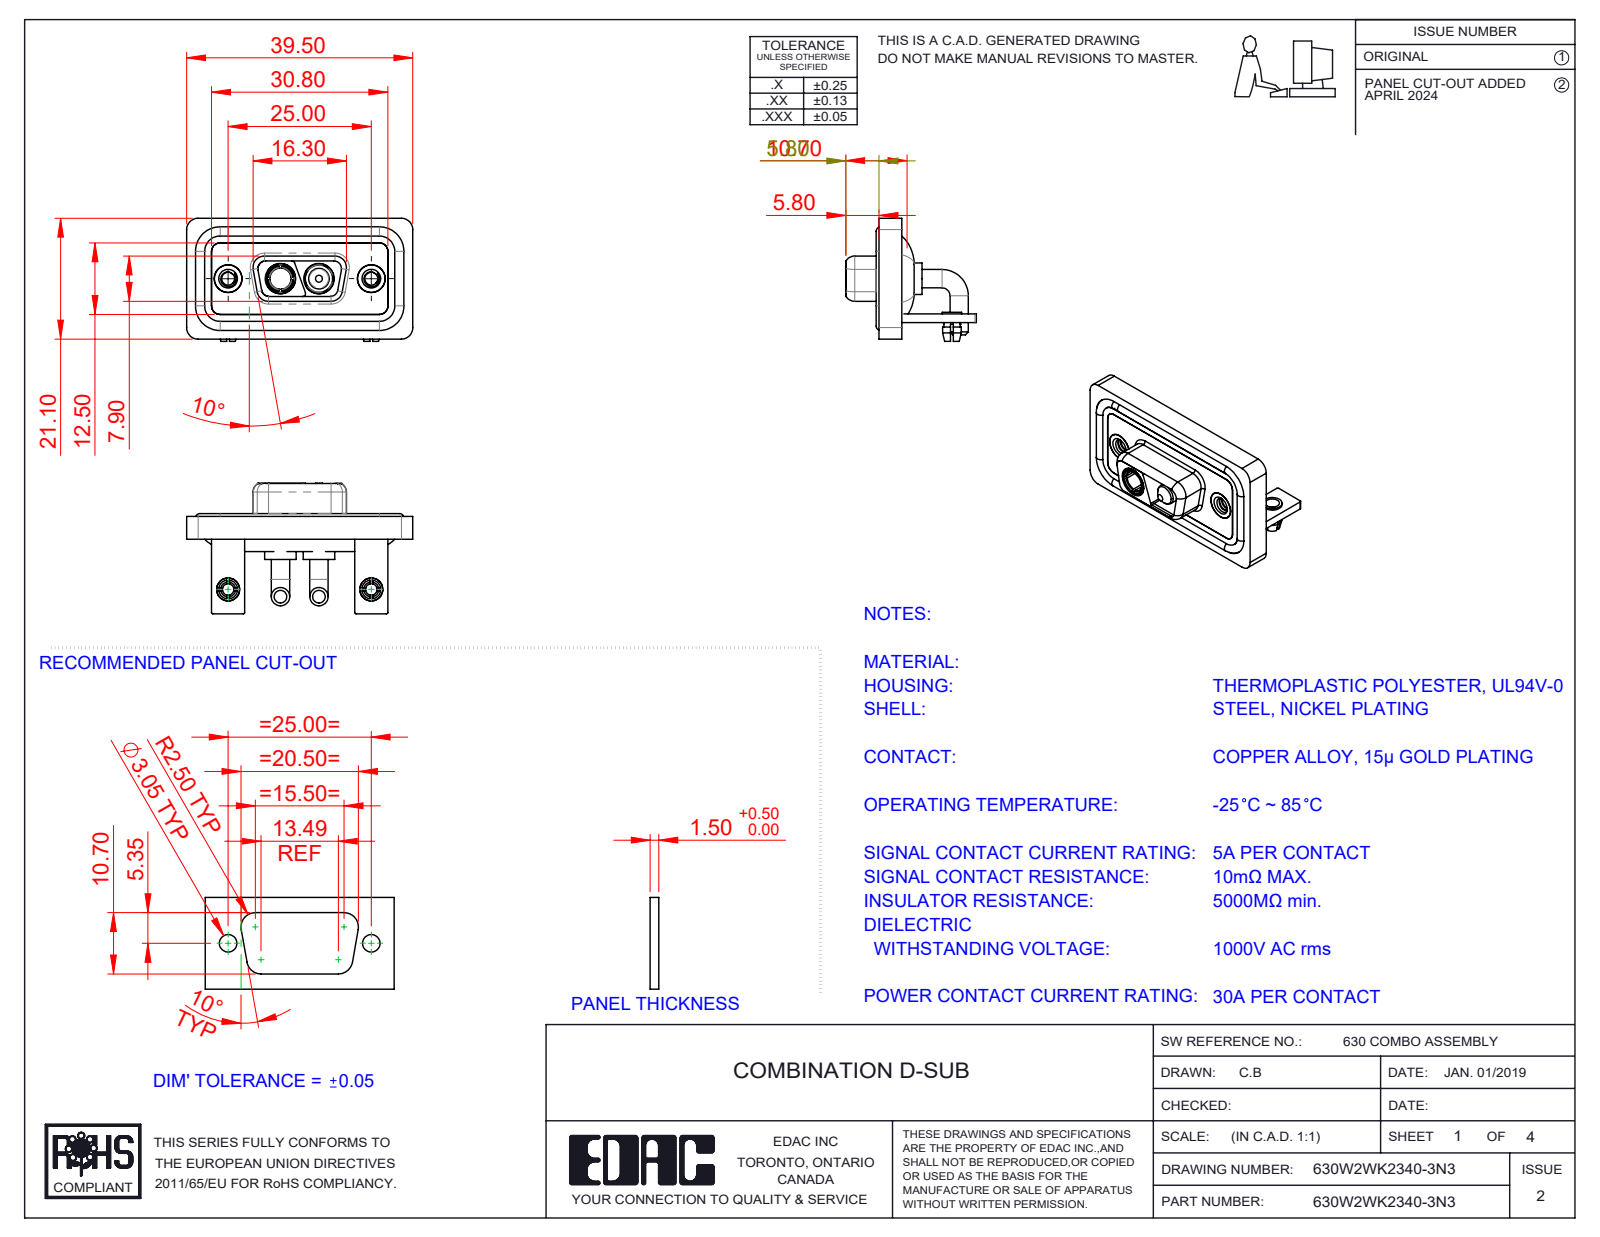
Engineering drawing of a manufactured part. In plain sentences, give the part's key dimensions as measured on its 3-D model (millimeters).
The part is named "630Combo Board Lock_50 Contacts; 630Combo Waterproof Housing_09 Contacts; 630Combo Threaded Rivet_2; 630W2WK2340-3N3 (+6 more)". Its 3-D file was written by "SolidWorks 2023 (CONFIG_CONTROL_DESIGN)". It is 15 solids with 648 faces: 212 planar, 291 cylindrical and 145 other. Overall it measures 39.5 by 22.8 by 21.5 millimeters. Its volume is 5 165 cubic millimeters and its surface area 8 477 square millimeters. Round holes: 4 of diameter 4.85, 2 of diameter 2, 2 of diameter 2.26, 2 of diameter 2.5, 2 of diameter 3.2, 2 of diameter 4, 2 of diameter 4.05, 2 of diameter 5, 2 of diameter 5.3, 1 of diameter 3.7. Round bosses or shafts: 4 of diameter 3.2, 4 of diameter 1.6, 2 of diameter 5.5, 2 of diameter 5.2, 2 of diameter 4.95, 2 of diameter 4.8, 2 of diameter 4.75, 2 of diameter 4. Partial cylindrical surfaces (rounded edges, fillets, slot ends): 19 of radius 2, 18 of radius 1.5, 16 of radius 0.25, 8 of radius 1.35, 8 of radius 1.6, 7 of radius 0.5, 4 of radius 0.6, 4 of radius 0.65. The main face-to-face distances are 0.4, 2.9, 1.5, 1.1, 3.7, 1.8, 0.8, 2.5, 1.6, 3.1. The hole center spacings are 9.14, 15.86, 25, 6.72.
